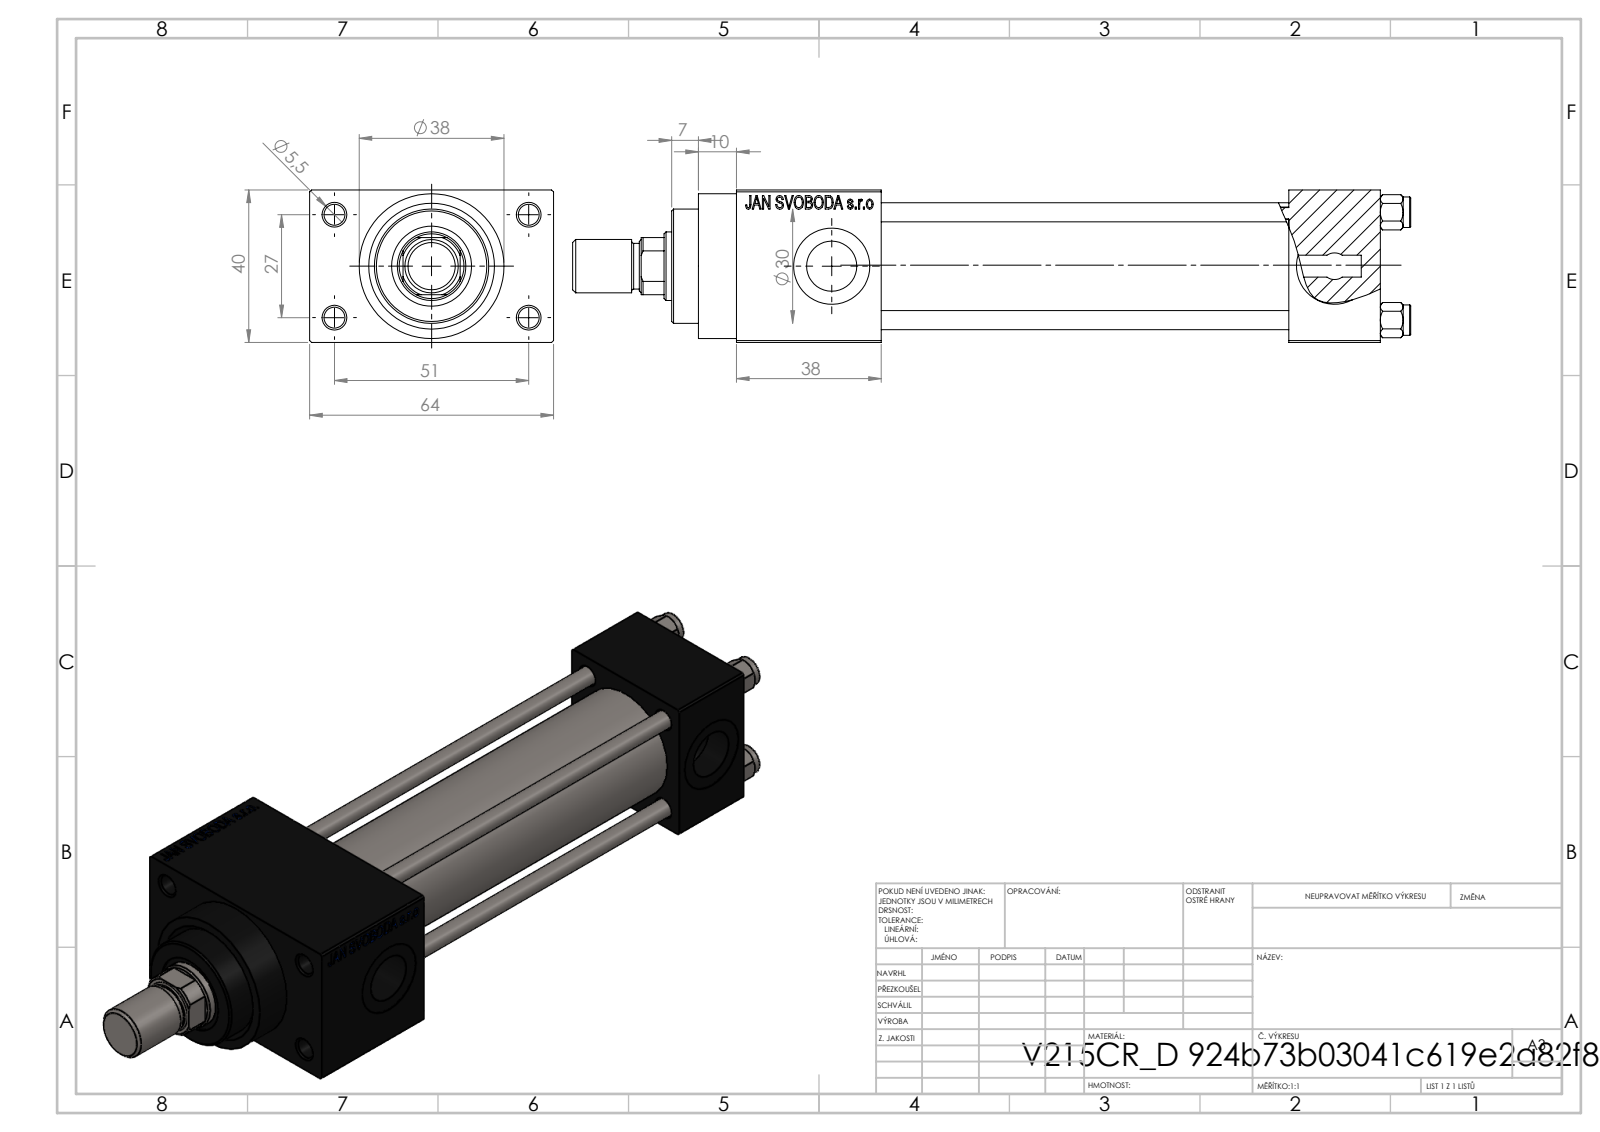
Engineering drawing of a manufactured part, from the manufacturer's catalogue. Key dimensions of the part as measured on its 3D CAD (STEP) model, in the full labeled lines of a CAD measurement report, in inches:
Part name (STEP PRODUCT): ROD_END_AH; V215CR_D_TYCINKA; NUT_M5_D; V215CR_D_Body (+2 more)
STEP written by: SolidWorks 2019 (CONFIG_CONTROL_DESIGN)
Units: inches
Bodies: 12 solids, 1115 faces (499 planar, 90 cylindrical, 526 other)
Overall size (bounding box): 8.661 × 2.52 × 1.575
Volume: 13.29 in³ · Surface area: 129.3 in²
Round holes (diameter × count): ⌀0.197 ×4, ⌀0.217 ×4, ⌀0.787 ×3, ⌀0.276 ×2, ⌀0.518 ×2, ⌀0.335 ×1, ⌀0.709 ×1, ⌀0.827 ×1, ⌀0.984 ×1, ⌀1.181 ×1
Round bosses / shafts (diameter × count): ⌀0.315 ×4, ⌀1.496 ×1, ⌀1.22 ×1, ⌀0.551 ×1, ⌀0.472 ×1
Partial cylindrical surfaces — rounded edges, fillets, slot ends (radius × count): R0.335 ×1
Main face-to-face distances: 1.575, 0.472, 4.213, 0.945, 5.157, 2.047, 1.496, 6.654, 5.709, 2.52
Hole centre spacings: 0.448, 0.788, 1.114, 1.136, 1.177, 1.561, 1.903, 1.063
